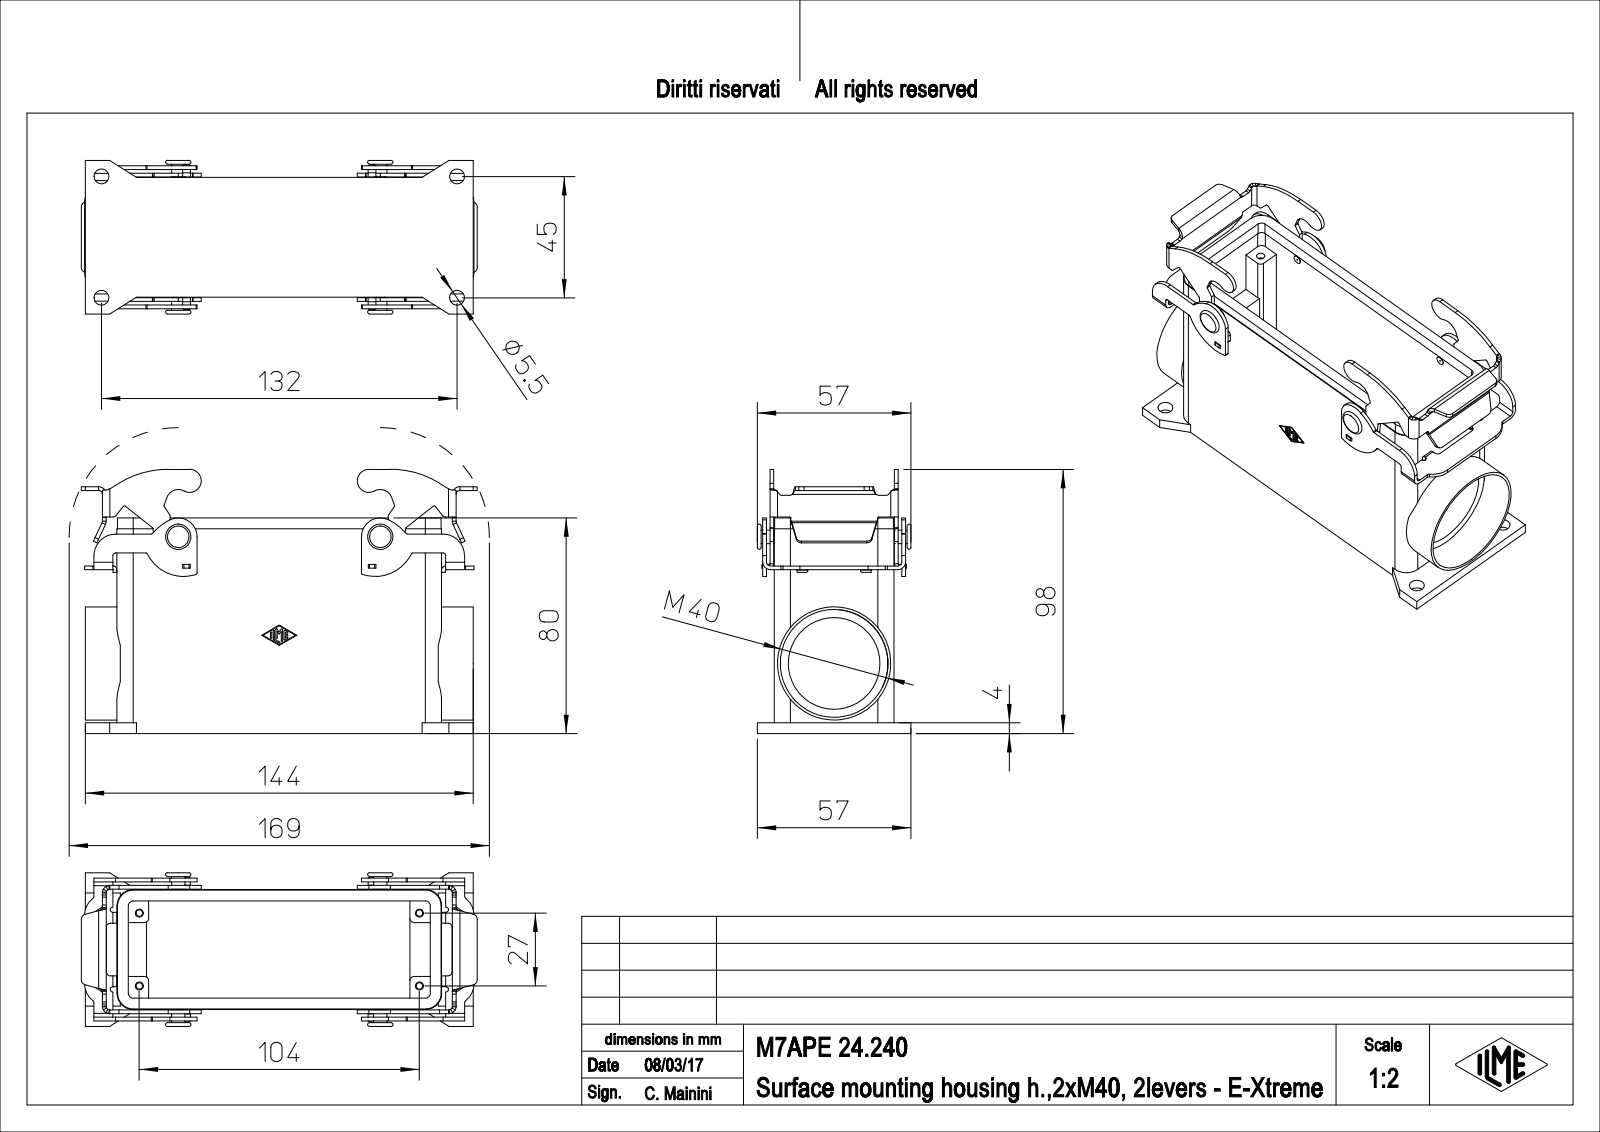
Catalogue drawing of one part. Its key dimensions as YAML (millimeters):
part_name: "M7APE_24.240"
step_written_by: "PTC Creo Elements/Direct Modeling 19.0E 27-Jun-2016 (C) Parametric Technology GmbH (AUTOMOTIVE_DESIGN)"
units: millimeters
bodies: {solids: 1, faces: 615, planar: 299, cylindrical: 272, other: 44}
overall_size: [146.97, 98, 57]
volume: 141256
surface_area: 83209
round_holes:
  - {diameter: 2.46, count: 4}
  - {diameter: 3, count: 4}
  - {diameter: 5.5, count: 4}
  - {diameter: 3.5, count: 2}
  - {diameter: 34, count: 1}
  - {diameter: 40, count: 1}
round_bosses_or_shafts:
  - {diameter: 5, count: 2}
  - {diameter: 3.2, count: 2}
  - {diameter: 3, count: 2}
  - {diameter: 42, count: 1}
partial_cylinders:
  - {radius: 0.5, count: 22}
  - {radius: 1, count: 18}
  - {radius: 0.25, count: 16}
  - {radius: 1.5, count: 14}
  - {radius: 2, count: 12}
  - {radius: 1.4, count: 10}
  - {radius: 2.8, count: 10}
  - {radius: 8, count: 6}
face_to_face_distances: [4, 40.5, 44.5, 36.5, 1.4, 2.7, 48.9, 11.75, 8.25, 1.55]
hole_center_spacings: [16.64, 38.63, 118.34, 123.37, 27, 45, 104, 107.45]
